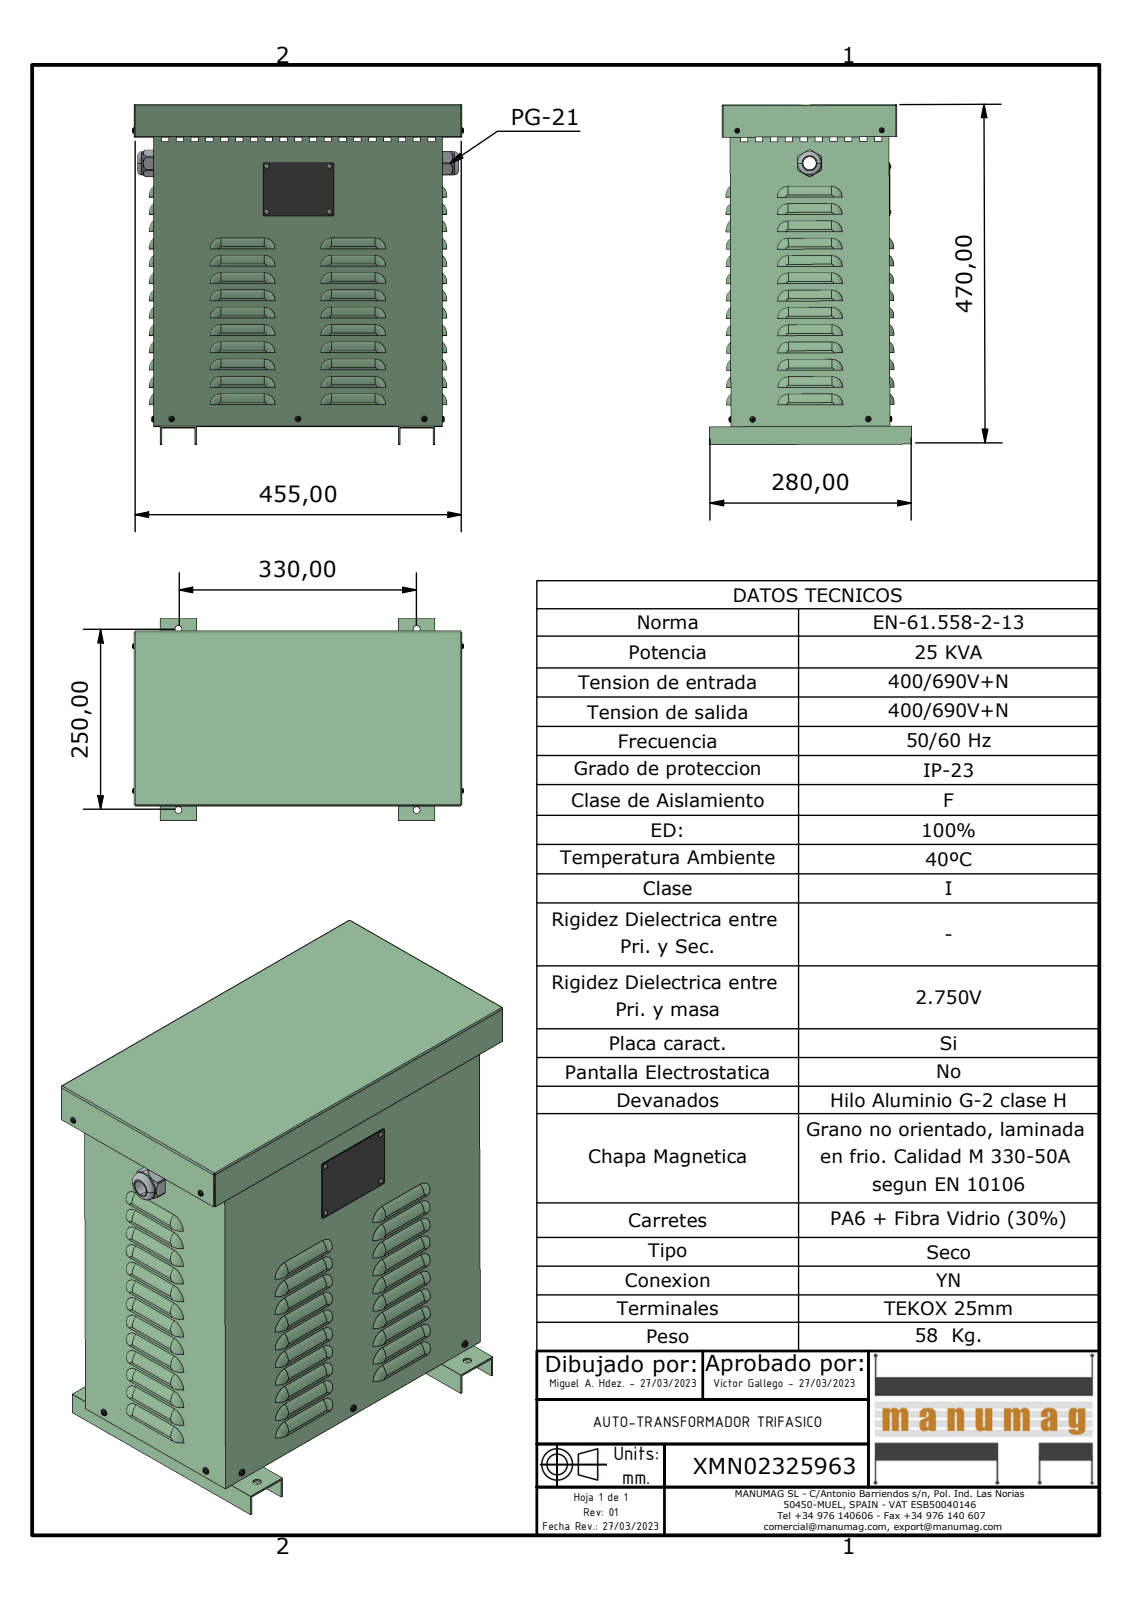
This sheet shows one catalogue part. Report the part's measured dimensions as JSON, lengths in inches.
{"part_name": "XMN02325963; JE015 - JE020 - JE025 NACIONAL CUERPO; JE015 - JE020 - JE025 NACIONAL BASE; JE015 - JE020 - JE025 NACIONAL PATA (+6 more)", "step_written_by": "Autodesk Inventor 2023 (AUTOMOTIVE_DESIGN)", "units": "inches", "bodies": {"solids": 26, "faces": 2110, "planar": 1086, "cylindrical": 450, "other": 574}, "overall_size": [18.596, 18.076, 11.027], "volume_in3": 101, "surface_area_in2": 2761, "round_holes": [[0.177, 12], [0.157, 6], [0.378, 4], [0.709, 1], [1.181, 1]], "round_bosses_or_shafts": [[0.157, 8], [0.143, 8], [0.126, 4], [0.138, 2], [0.125, 2], [1.276, 1], [1.122, 1], [1.114, 1]], "partial_cylinders_radius": [[0.551, 118], [0.157, 49], [0.591, 49], [0.118, 16], [0.177, 16], [0.059, 8], [0.079, 4], [0.732, 1]], "face_to_face_distances": [0.059, 8.602, 8.543, 17.52, 15.689, 8.661, 15.63, 17.579, 15.748, 17.461], "hole_center_spacings": [6.89, 2.48, 13.78, 0.02, 3.425, 3.445, 4.229, 4.245]}
